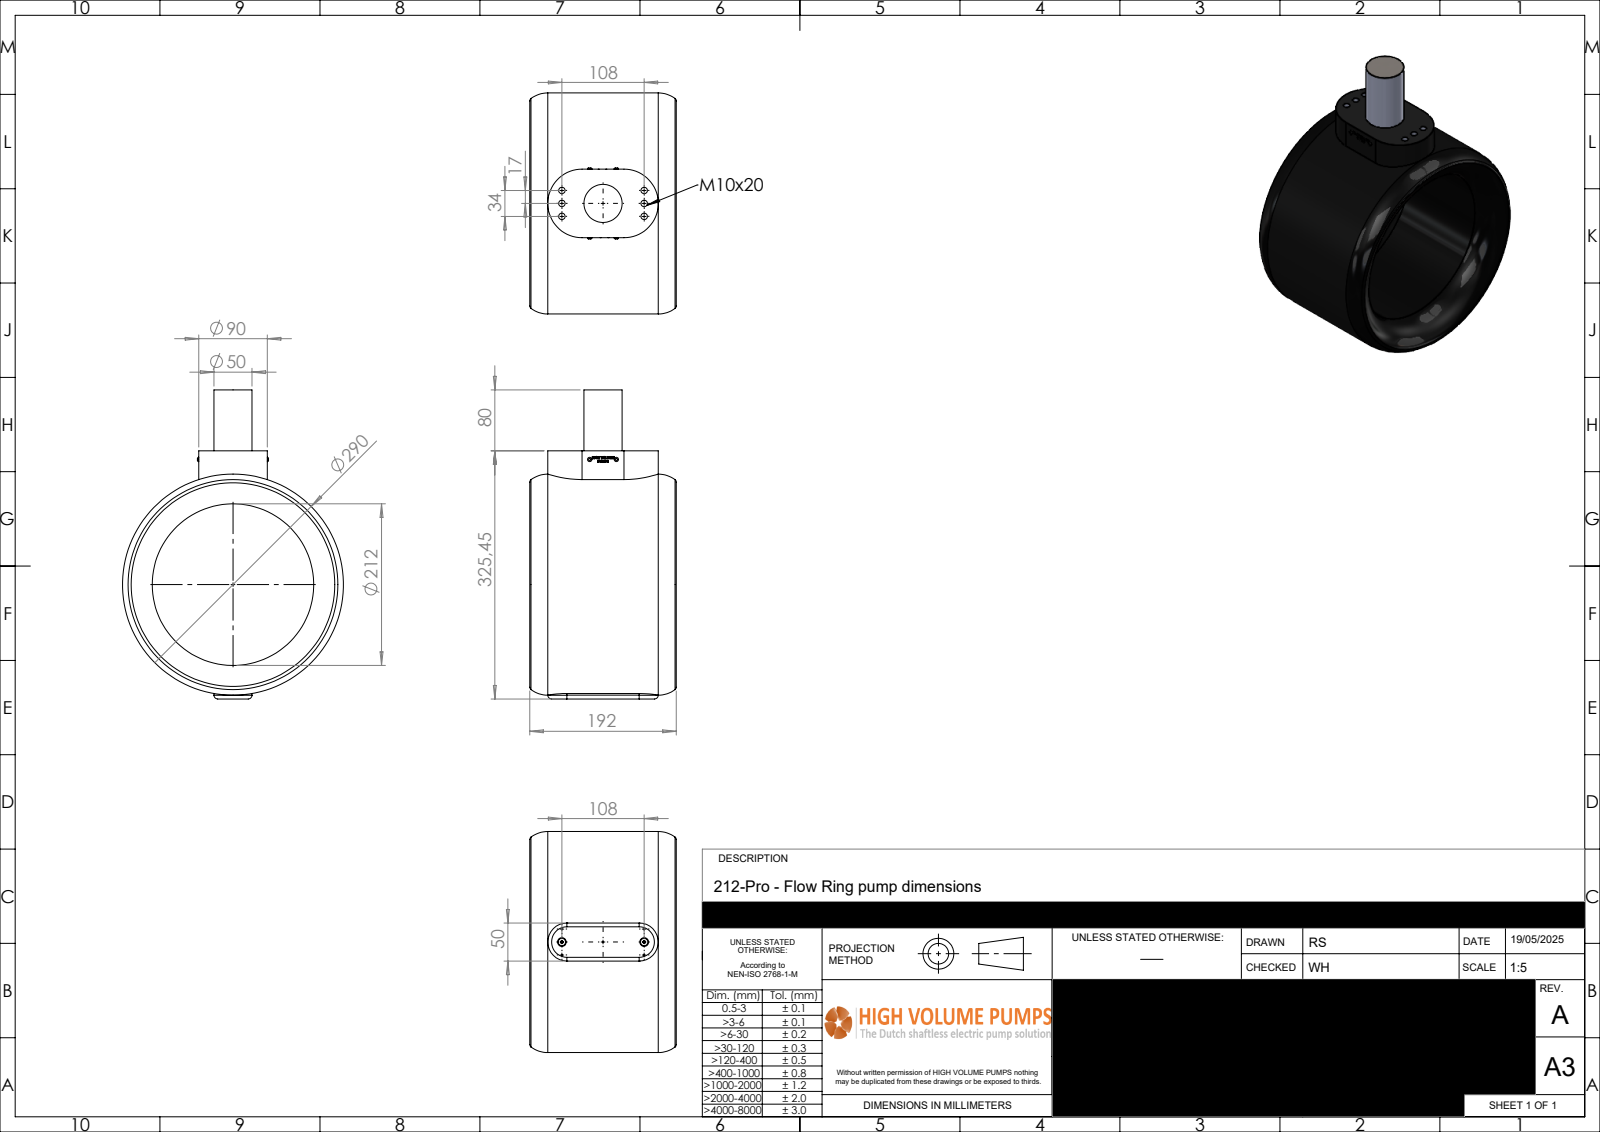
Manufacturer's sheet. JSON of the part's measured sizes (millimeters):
{"part_name": "P-212-530-rev-A-FR", "step_written_by": "SolidWorks 2024 (AUTOMOTIVE_DESIGN)", "units": "millimeters", "bodies": {"solids": 1, "faces": 477, "planar": 311, "cylindrical": 26, "other": 140}, "overall_size": [405.45, 290, 192.22], "volume_mm3": 5993000, "surface_area_mm2": 364671, "round_holes": [[8.5, 6], [5.3, 2], [212, 1]], "round_bosses_or_shafts": [[9.64, 2], [5.7, 2], [5, 2], [290, 1], [50, 1]], "partial_cylinders_radius": [[5, 2], [25, 2], [45, 2]], "face_to_face_distances": [325.45, 405.45, 80, 90, 20, 70, 305.45, 100, 50, 0.43], "hole_center_spacings": [17, 109.33, 108, 34, 113.23]}
